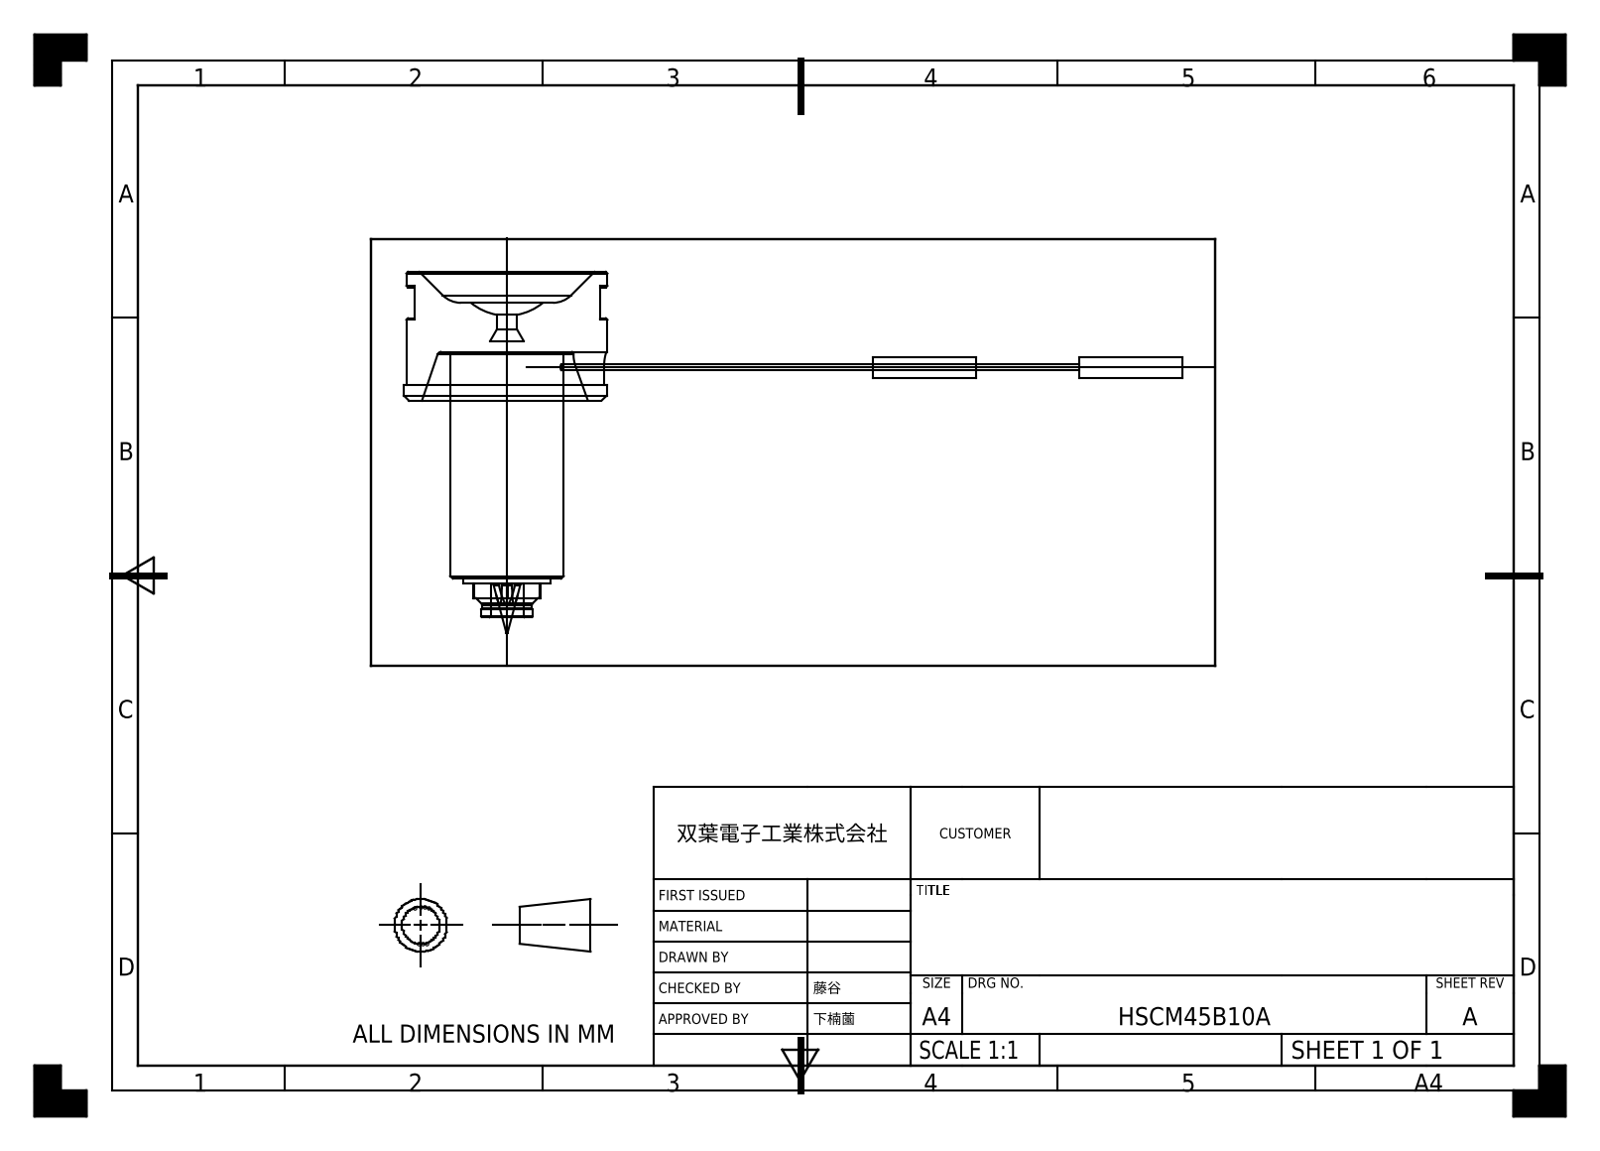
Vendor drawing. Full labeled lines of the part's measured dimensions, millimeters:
Part name (STEP PRODUCT): HSCM45B10A
STEP written by: SIEMENS PLM Software NX 2023 (AUTOMOTIVE_DESIGN)
Units: millimetres
Bodies: 1 solid, 75 faces (30 planar, 23 cylindrical, 22 other)
Overall size (bounding box): 151 × 70 × 40
Volume: 36 930 mm³ · Surface area: 11 046 mm²
Round holes (diameter × count): ⌀4 ×1, ⌀6.35 ×1
Round bosses / shafts (diameter × count): ⌀4 ×2, ⌀1.2 ×2, ⌀40 ×1, ⌀39 ×1, ⌀22 ×1, ⌀16.9 ×1, ⌀10 ×1, ⌀9.6 ×1
Partial cylindrical surfaces — rounded edges, fillets, slot ends (radius × count): R2.8 ×3, R3 ×2, R7.45 ×1
Main face-to-face distances: 9.5, 25, 15.5, 45, 59.5, 44, 34.5, 3, 6, 19
